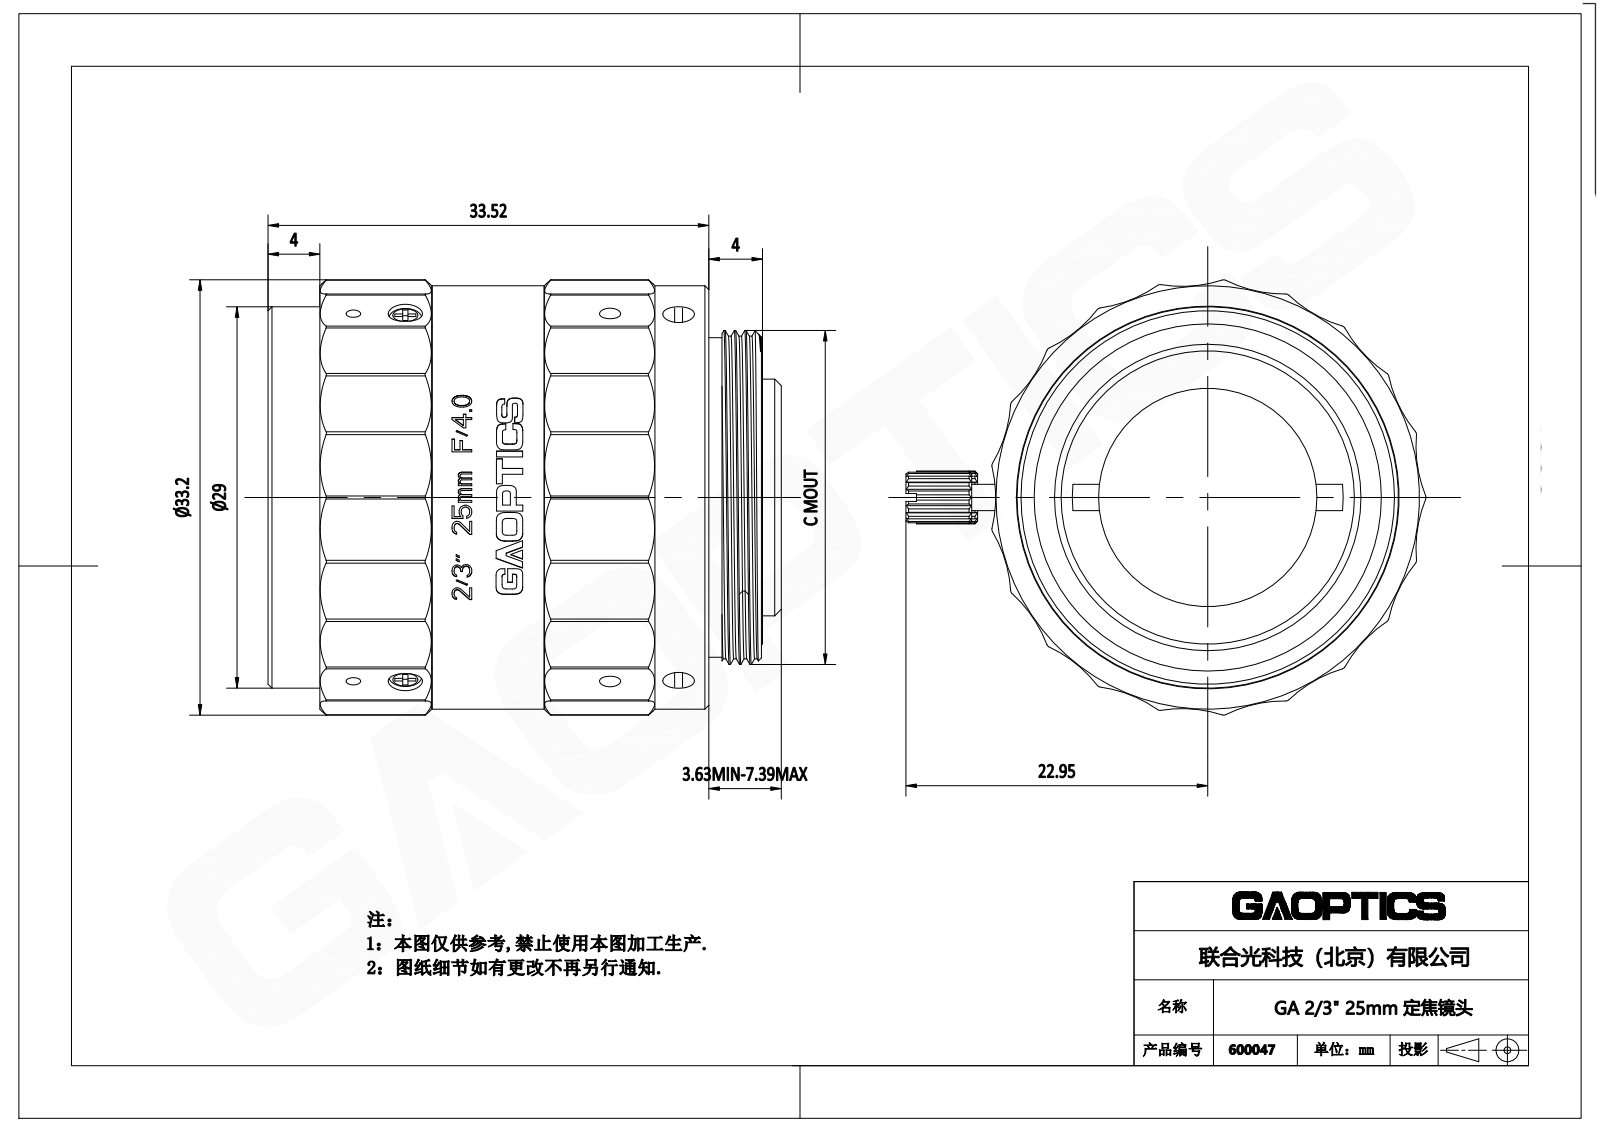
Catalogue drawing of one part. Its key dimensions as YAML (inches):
part_name: "600047"
step_written_by: "SolidWorks 2019 (CONFIG_CONTROL_DESIGN)"
units: inches
bodies: {solids: 13, faces: 1498, planar: 523, cylindrical: 143, other: 832}
overall_size: [1.557, 1.537, 1.304]
volume: 1.319
surface_area: 21.55
round_holes:
  - {diameter: 0.043, count: 3}
  - {diameter: 0.059, count: 3}
  - {diameter: 0.063, count: 3}
  - {diameter: 0.094, count: 3}
  - {diameter: 0.102, count: 3}
  - {diameter: 0.433, count: 1}
  - {diameter: 0.654, count: 1}
  - {diameter: 0.878, count: 1}
  - {diameter: 0.882, count: 1}
  - {diameter: 0.988, count: 1}
  - {diameter: 1.039, count: 1}
  - {diameter: 1.071, count: 1}
round_bosses_or_shafts:
  - {diameter: 0.118, count: 3}
  - {diameter: 0.098, count: 3}
  - {diameter: 0.055, count: 3}
  - {diameter: 0.079, count: 2}
  - {diameter: 1.268, count: 1}
  - {diameter: 1.142, count: 1}
  - {diameter: 1.02, count: 1}
  - {diameter: 1, count: 1}
partial_cylinders:
  - {radius: 0.394, count: 13}
  - {radius: 0.012, count: 1}
  - {radius: 0.632, count: 1}
face_to_face_distances: [0.161, 0.335, 0.032, 0.039, 1.202, 0.337, 0.378, 0.682, 0.217, 0.715]
hole_center_spacings: [0.156, 0.205, 0.613, 0.769, 0.818, 0.974]
